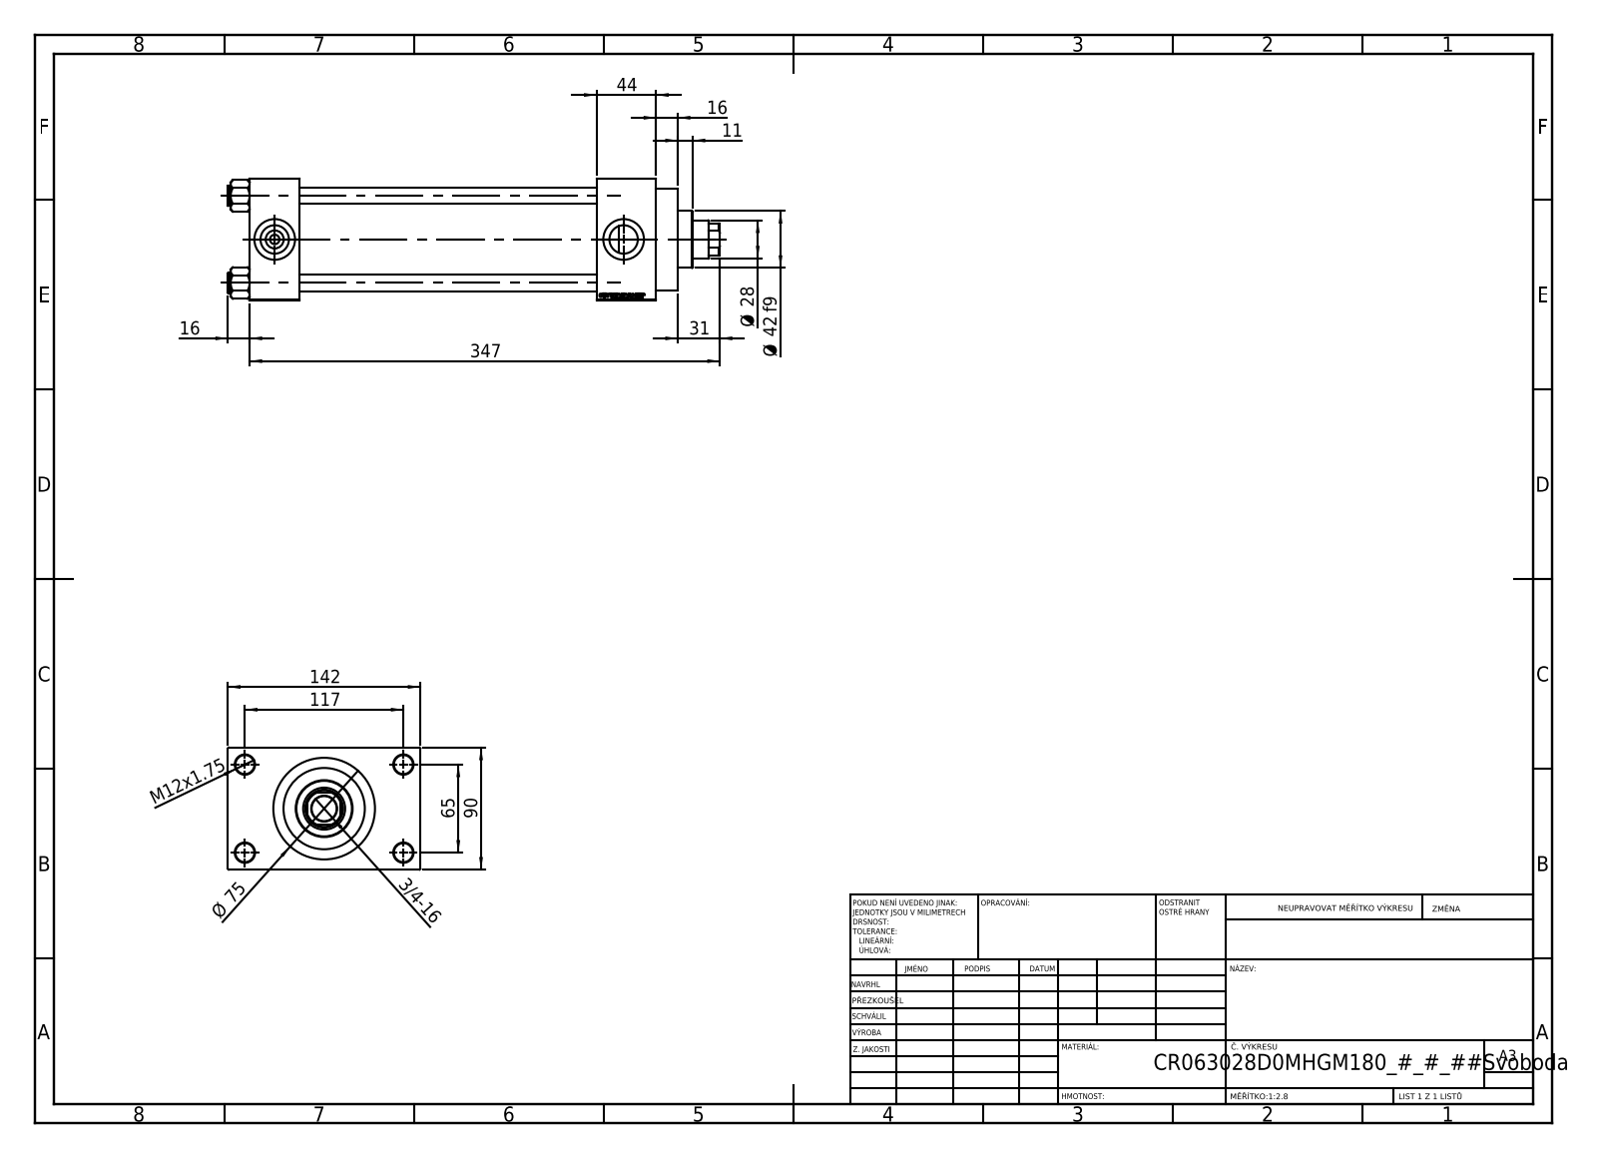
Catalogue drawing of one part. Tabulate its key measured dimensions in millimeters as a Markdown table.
| quantity | value |
| --- | --- |
| part name | V215CR_D_TYCINKA; V215CR_D_Body; V215CR_VCP_D; NUT_M5_D (+1 more) |
| STEP written by | SolidWorks 2019 (CONFIG_CONTROL_DESIGN) |
| units | millimeters |
| bodies | 11 solids, 1103 faces (497 planar, 88 cylindrical, 518 other) |
| overall size | 363 × 142 × 90 |
| volume | 1 367 000 mm³ |
| surface area | 304 866 mm² |
| round holes (diameter × count) | 12 × 4, 14 × 4, 7 × 2, 20.96 × 2, 30 × 2, 18.5 × 1, 28 × 1, 31 × 1, 50 × 1, 60 × 1, 63 × 1 |
| round bosses / shafts (diameter × count) | 15 × 4, 75 × 1, 69 × 1, 42 × 1 |
| partial cylindrical surfaces (radius × count) | 13.5 × 1 |
| main face-to-face distances | 90, 219, 37, 256, 263, 300, 44, 26, 116, 16 |
| hole center spacings | 26.35, 45.47, 64.3, 66.92, 69.81, 90.65, 111.34, 65 |
